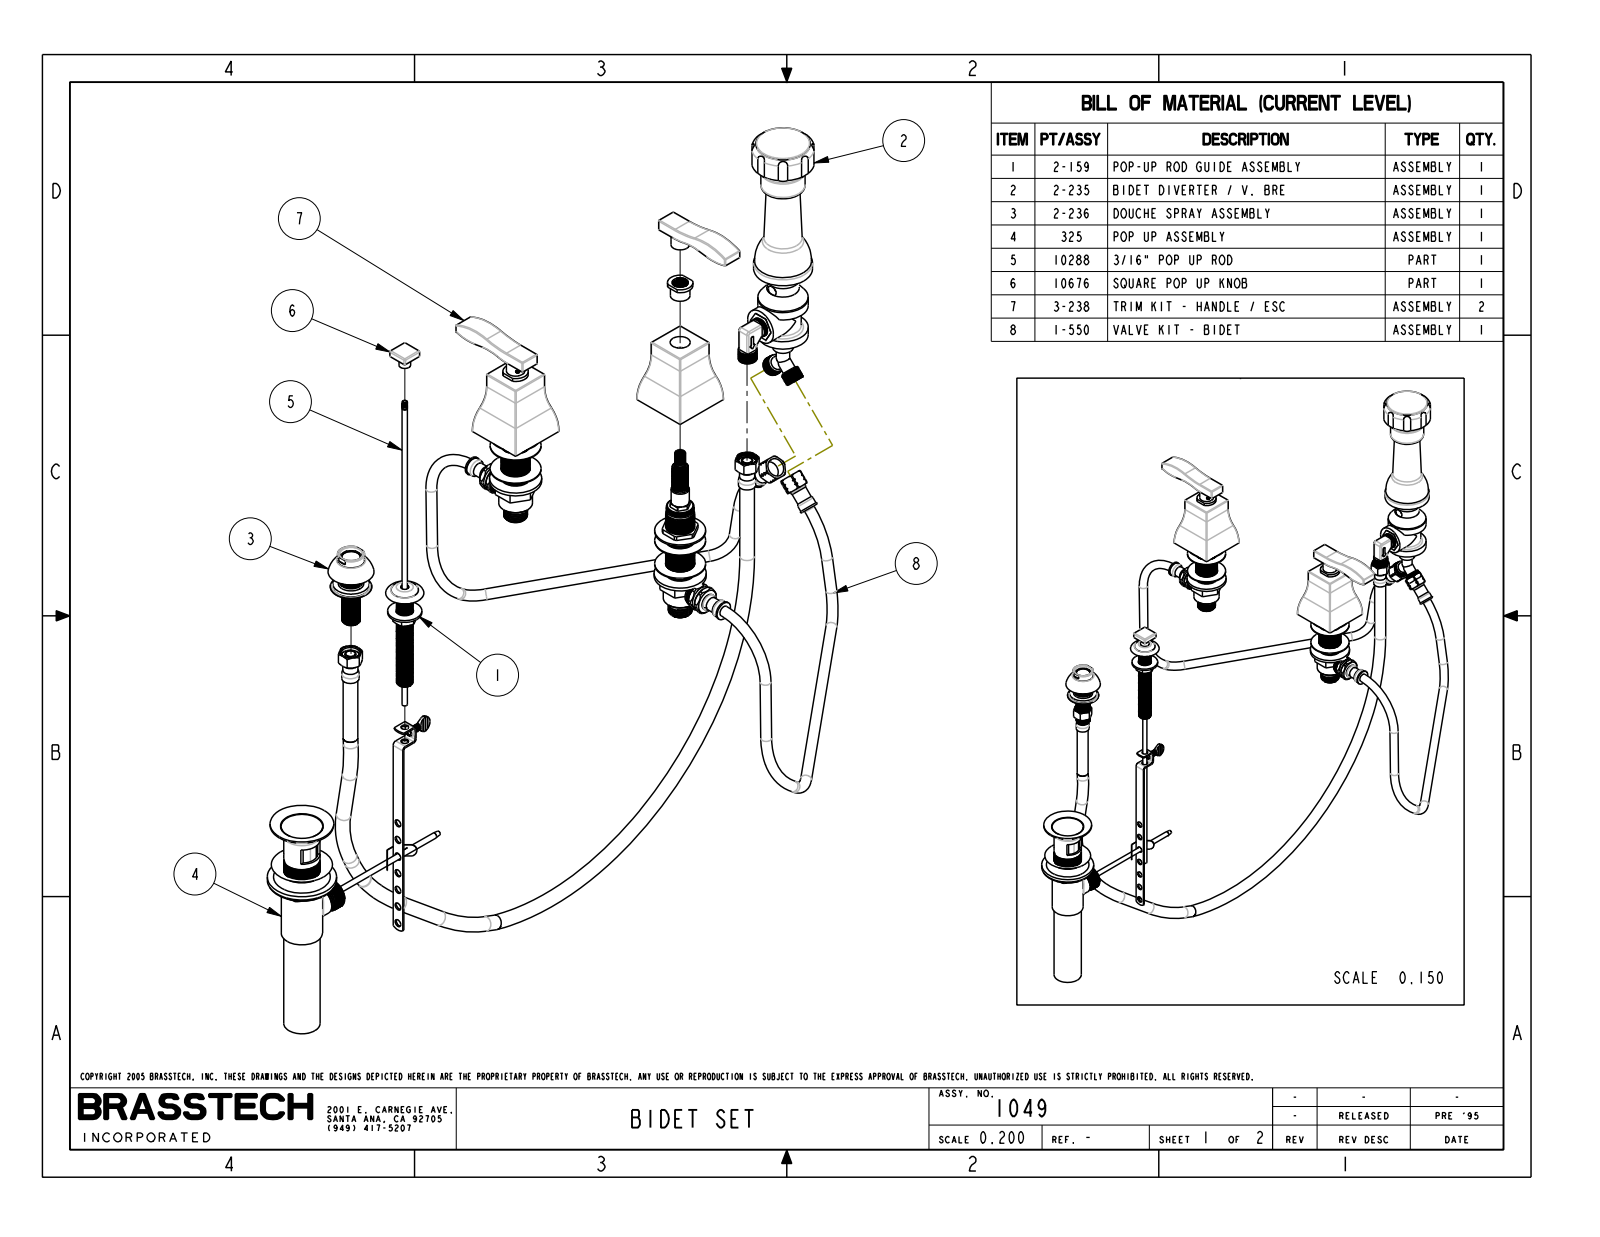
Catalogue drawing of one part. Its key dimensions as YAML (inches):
part_name: "1049_WEB"
step_written_by: "PRO/ENGINEER BY PARAMETRIC TECHNOLOGY CORPORATION, 2009300 (CONFIG_CONTROL_DESIGN)"
units: inches
bodies: {solids: 0, faces: 275, planar: 49, cylindrical: 114, other: 112}
overall_size: [22.855, 13.1, 5.353]
round_bosses_or_shafts:
  - {diameter: 0.63, count: 2}
  - {diameter: 2.025, count: 1}
  - {diameter: 1.52, count: 1}
  - {diameter: 0.926, count: 1}
  - {diameter: 0.4, count: 1}
partial_cylinders:
  - {radius: 0.03, count: 38}
  - {radius: 0.04, count: 12}
  - {radius: 0.21, count: 8}
  - {radius: 2.5, count: 8}
  - {radius: 2.75, count: 6}
  - {radius: 2, count: 4}
  - {radius: 0.437, count: 2}
  - {radius: 2.25, count: 2}
face_to_face_distances: [2.31, 0.348, 1.078, 1.425, 0.73, 3.468, 1.158, 8, 0.6, 2.43]
